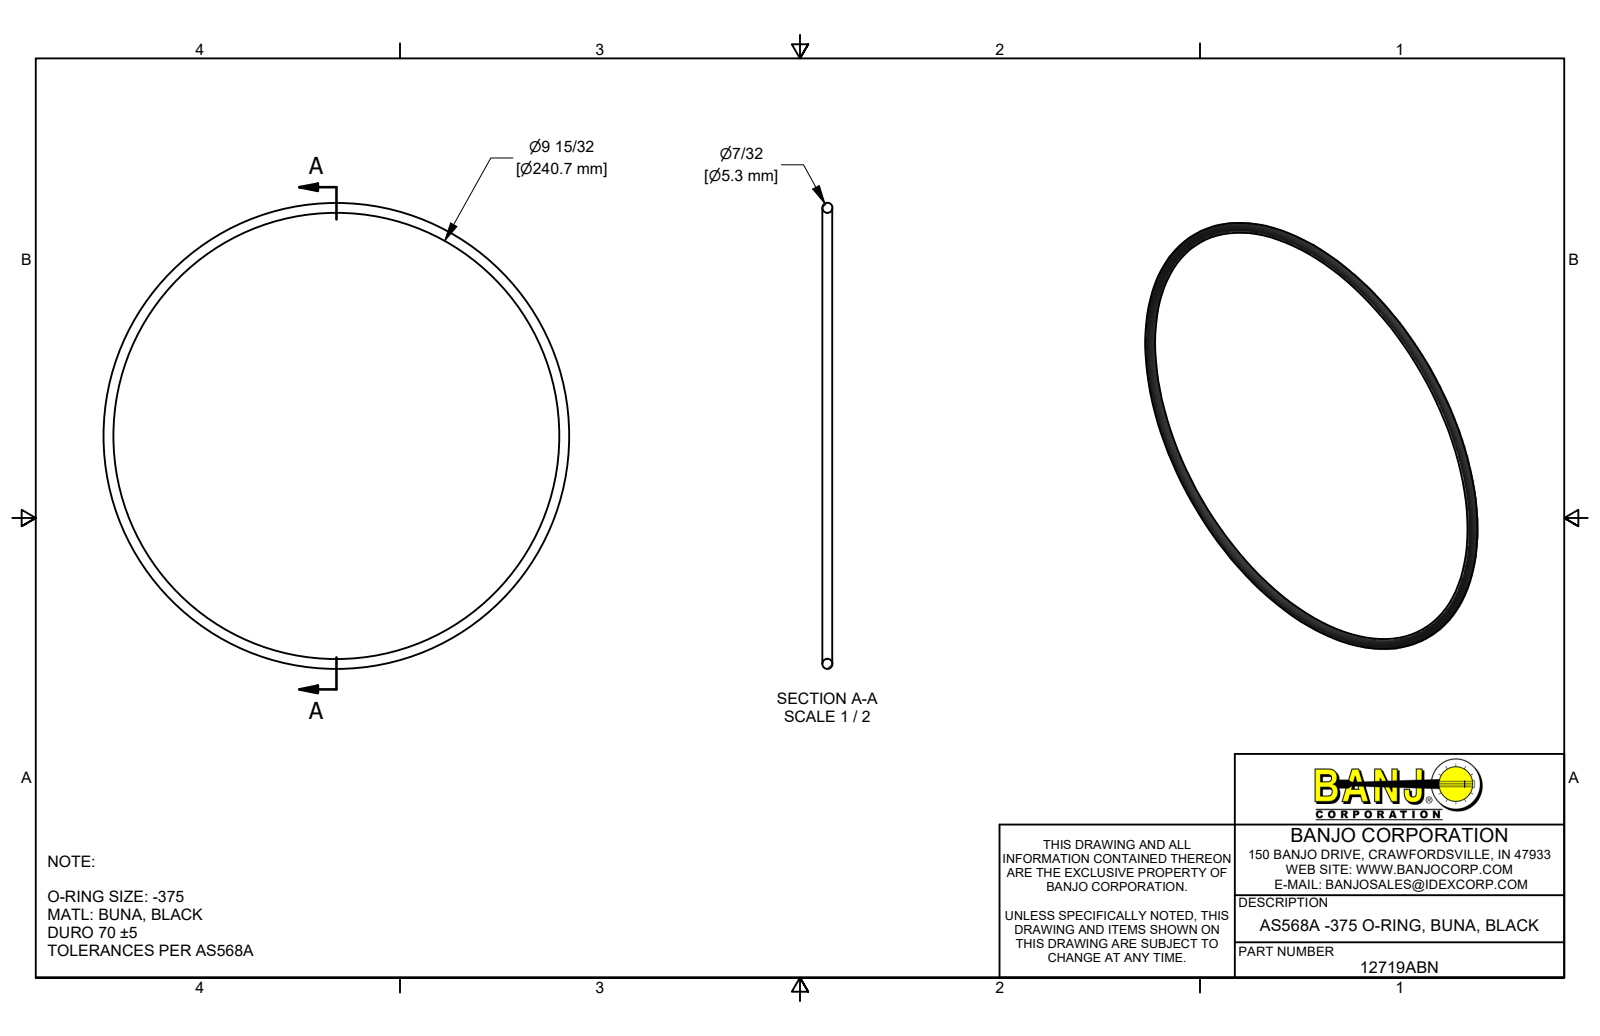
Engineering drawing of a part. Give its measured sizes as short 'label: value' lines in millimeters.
name: 12719ABN
written by: Autodesk Inventor 2019 (AUTOMOTIVE_DESIGN)
unit: mm
bodies: 1 solid, 1 faces (0 planar, 0 cylindrical, 1 other)
size: 251.3 × 251.3 × 5.3
volume: 17 270 mm³; area: 12 950 mm²
